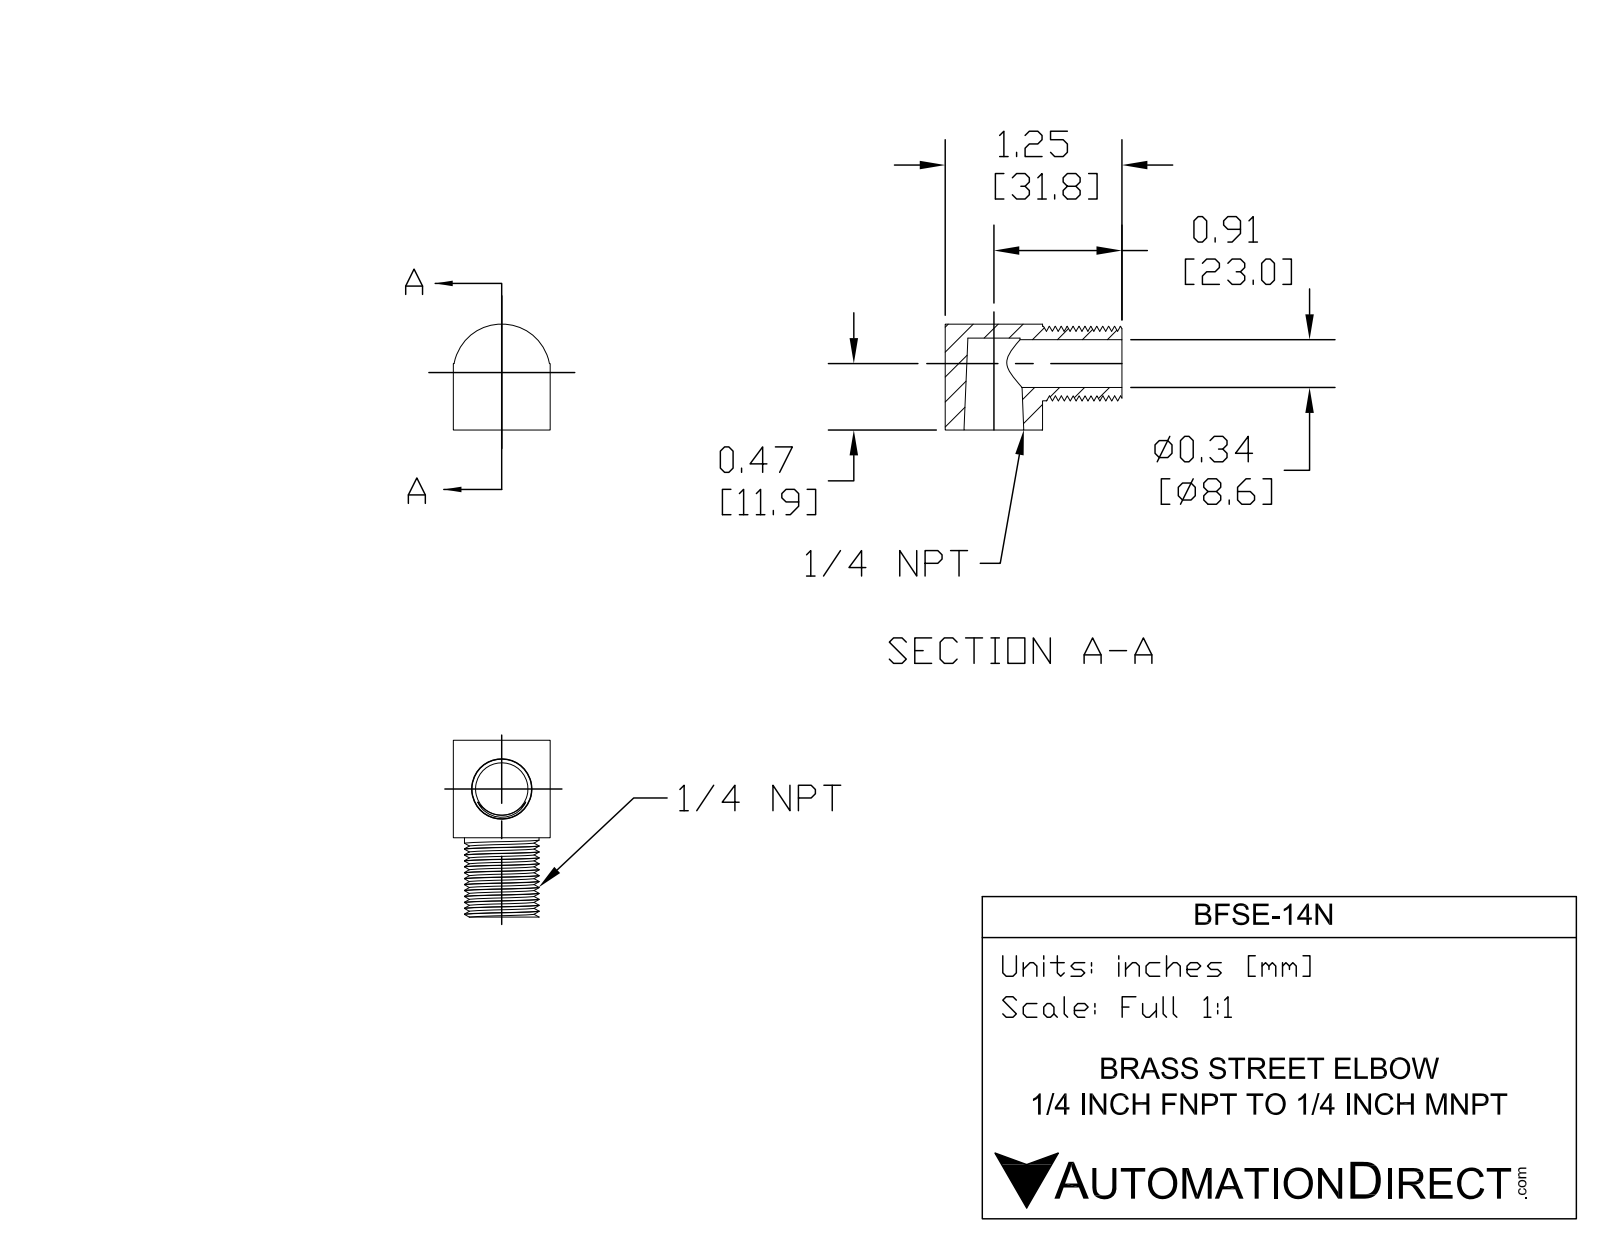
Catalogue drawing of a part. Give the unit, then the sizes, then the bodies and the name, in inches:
Units: inches
Overall size (bounding box): 1.252 × 0.75 × 0.686
Round holes (diameter × count): ⌀0.34 ×1
Round bosses / shafts (diameter × count): ⌀0.528 ×1
Partial cylindrical surfaces — rounded edges, fillets, slot ends (radius × count): R0.344 ×1
Main face-to-face distances: 0.686, 0.69, 0.65, 0.562, 1.252, 0.47, 0.18
Volume: 0.281 in³ · Surface area: 5.774 in²
Bodies: 1 solid, 45 faces (10 planar, 30 cylindrical, 5 other)
Part name (STEP PRODUCT): BFSE-14N
STEP written by: SolidWorks 2015 (CONFIG_CONTROL_DESIGN)
